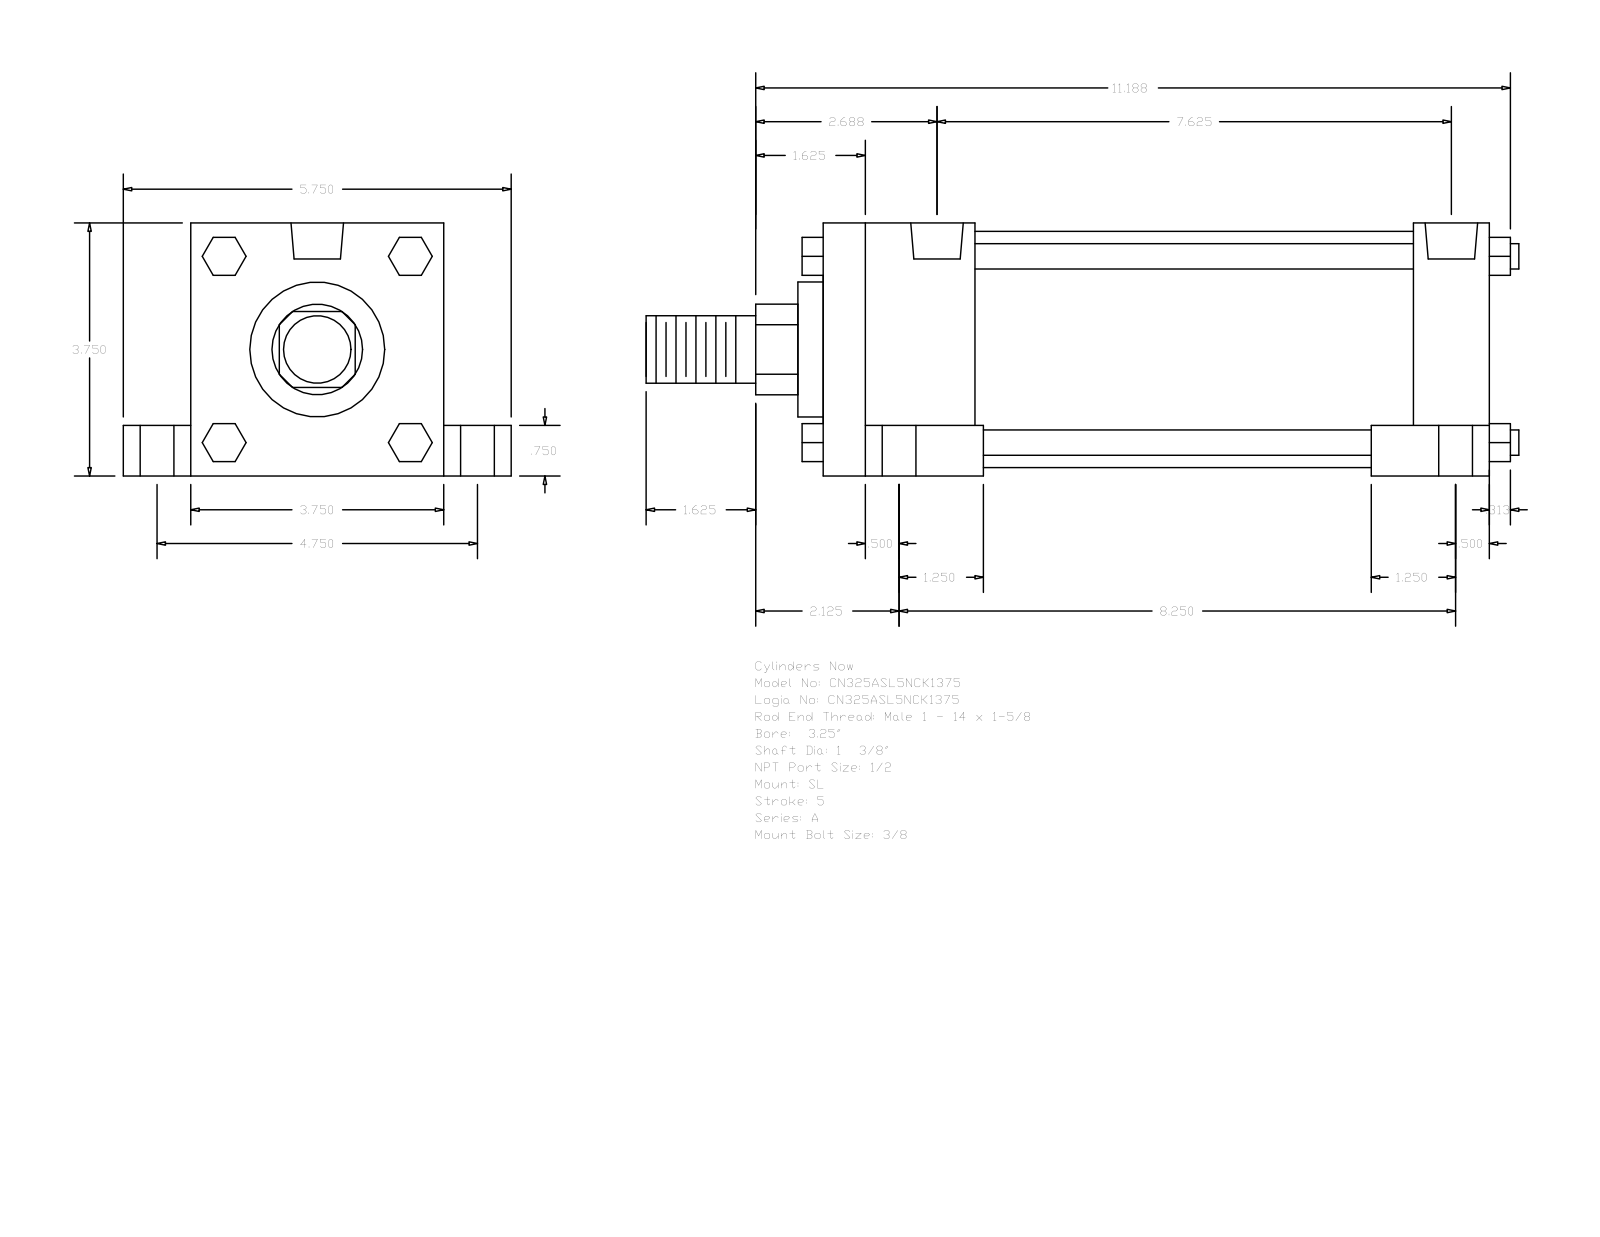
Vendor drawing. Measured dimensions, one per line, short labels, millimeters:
name: A_SL__0325_1.375
written by: GSSL Pune (CONFIG_CONTROL_DESIGN)
unit: mm
bodies: 0 solids, 150 faces (114 planar, 36 cylindrical, 0 other)
size: 328.61 × 146.05 × 95.25
holes: 4× ⌀8.73, 4× ⌀12.7, 4× ⌀19.05, 2× ⌀19.77
bosses: 4× ⌀9.53, 1× ⌀88.9, 1× ⌀50.8, 1× ⌀34.92, 1× ⌀25.4
rounds: 1× R17.06
face distances: 95.24, 250.83, 25.41, 120.65, 19.05, 76.19, 57.15, 28.58, 146.06, 222.25
hole spacings: 3.18, 60.35, 60.52, 62, 62.81, 120.66, 187.32, 190.5
